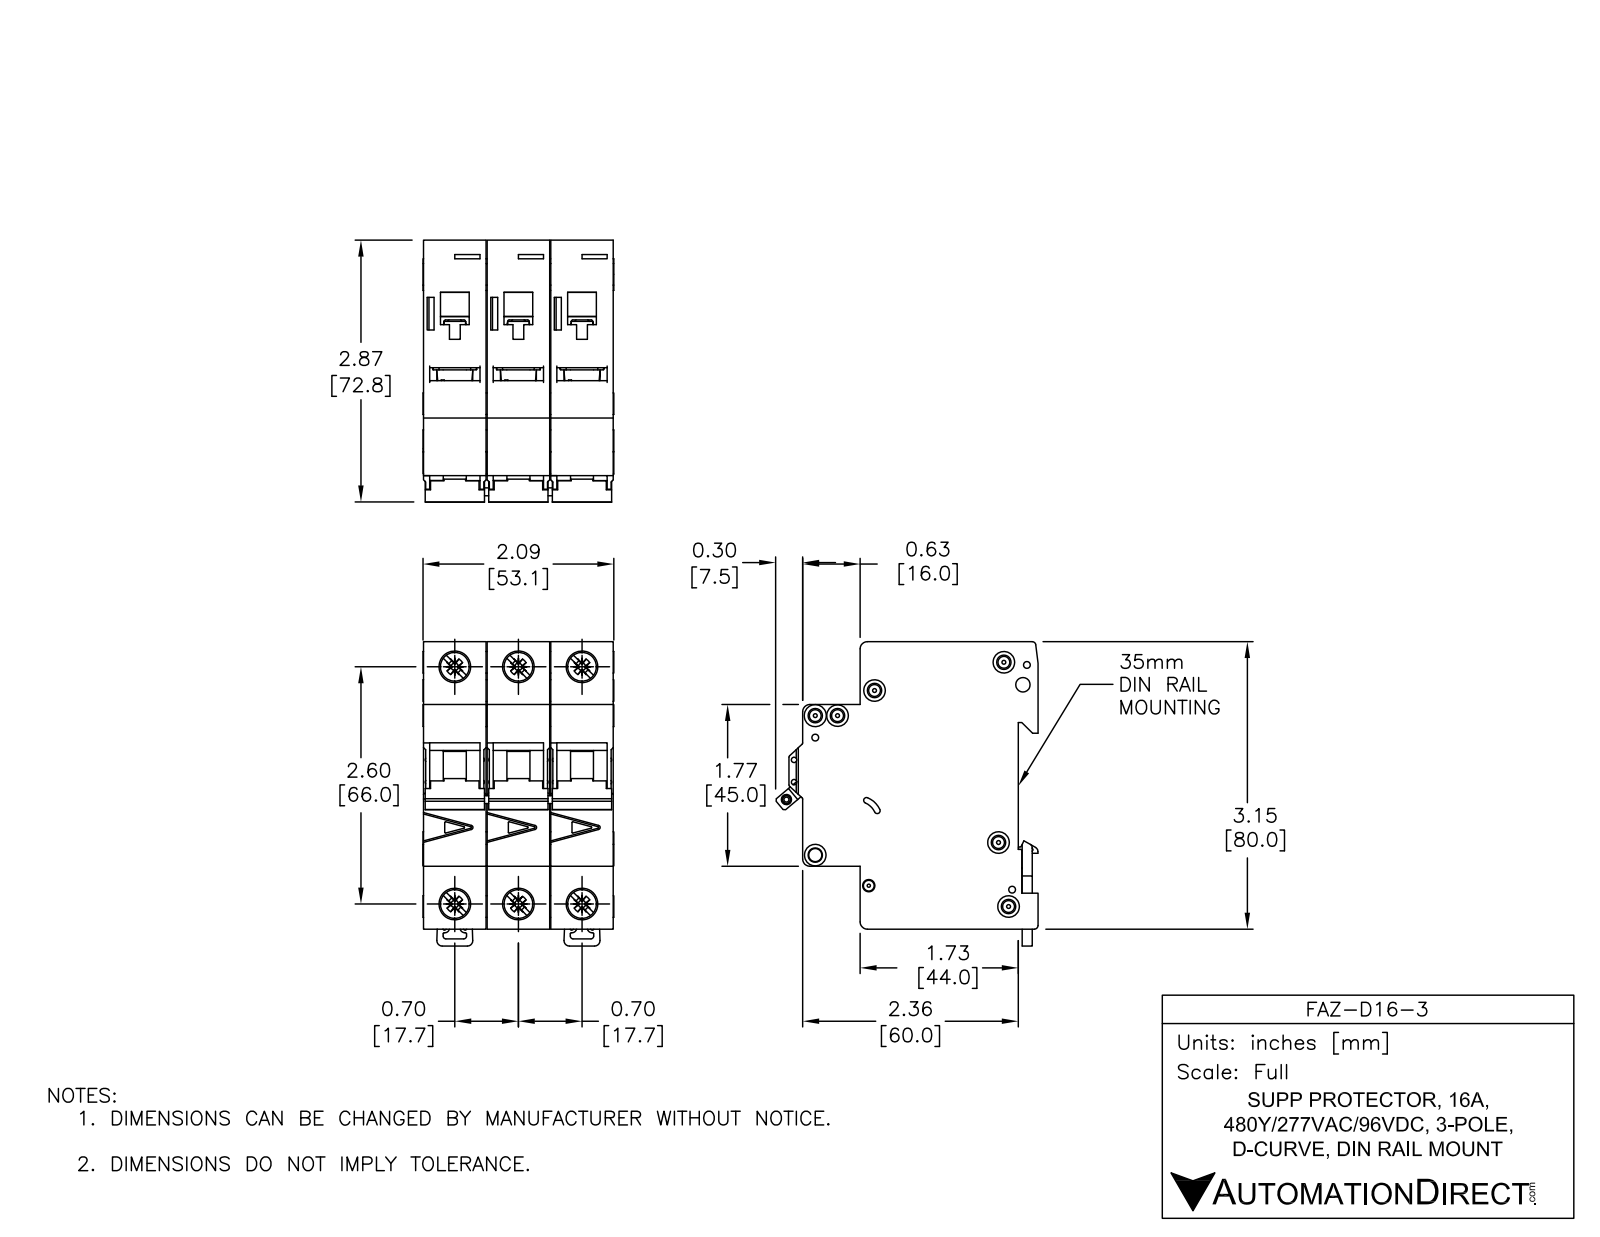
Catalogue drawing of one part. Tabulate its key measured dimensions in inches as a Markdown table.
| quantity | value |
| --- | --- |
| part name | FAZ-D16-3 |
| STEP written by | SolidWorks 2014 (AUTOMOTIVE_DESIGN) |
| units | inches |
| bodies | 11 solids, 1650 faces (697 planar, 590 cylindrical, 363 other) |
| overall size | 3.338 × 2.876 × 2.091 |
| volume | 13.71 in³ |
| surface area | 89.98 in² |
| round holes (diameter × count) | 0.142 × 6, 0.323 × 4, 0.075 × 3, 0.043 × 2, 0.059 × 2, 0.157 × 2, 0.281 × 2, 0.085 × 1, 0.087 × 1, 0.1 × 1, 0.13 × 1, 0.134 × 1 |
| round bosses / shafts (diameter × count) | 0.236 × 4, 0.098 × 3, 0.323 × 2 |
| partial cylindrical surfaces (radius × count) | 0.01 × 68, 0.02 × 25, 0.039 × 12, 0.079 × 12, 0.008 × 11, 0.071 × 3, 0.031 × 2, 0.118 × 2 |
| main face-to-face distances | 0.697, 0.689, 1.394, 1.386, 2.083, 0.705, 3.129, 0.217, 1.949, 1.732 |
| hole center spacings | 0.697, 2.69, 2.598, 0.244, 0.537, 1.394, 2.948, 0.189 |
